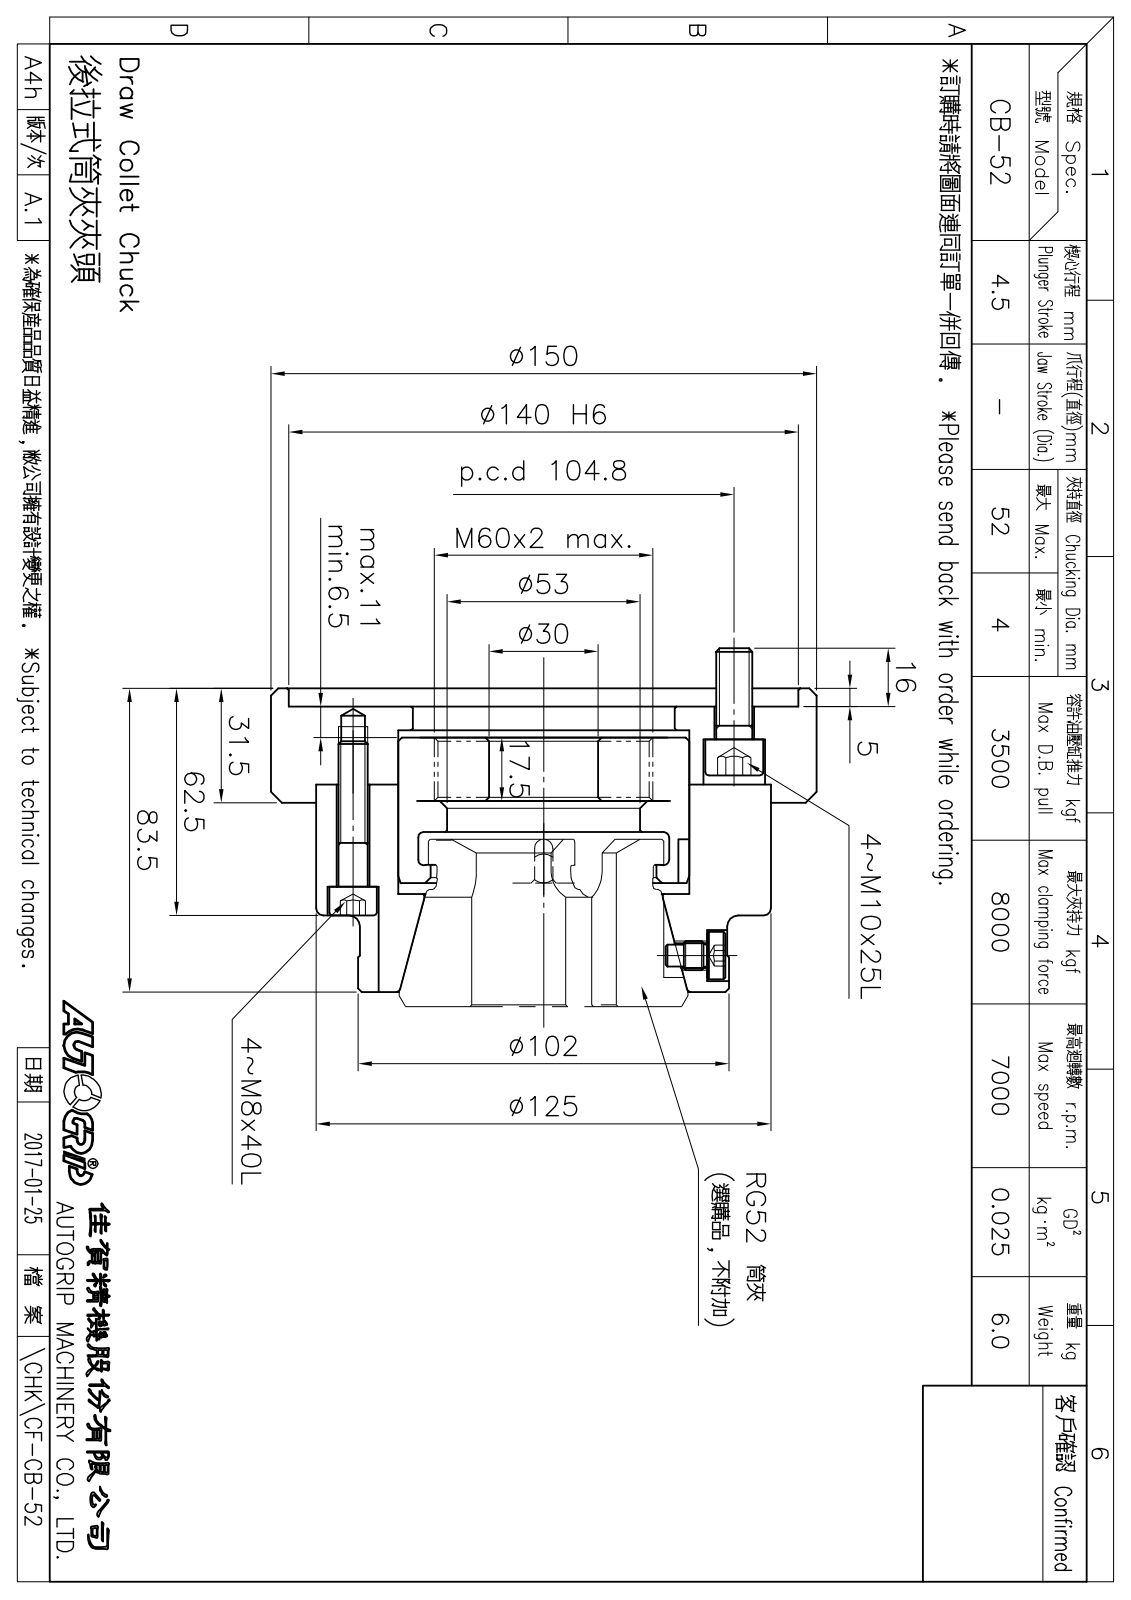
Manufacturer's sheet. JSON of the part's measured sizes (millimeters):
{"part_name": "CF-CB-52-03000; RG52-D40; CF-CB-52-01000; FSW320700 (+4 more)", "step_written_by": "SolidWorks 2020 (CONFIG_CONTROL_DESIGN)", "units": "millimeters", "bodies": {"solids": 13, "faces": 544, "planar": 209, "cylindrical": 167, "other": 168}, "overall_size": [150, 150, 100.95], "volume_mm3": 839910, "surface_area_mm2": 176692, "round_holes": [[5, 8], [6.5, 6], [6.8, 5], [14, 5], [9, 4], [11, 4], [17, 4], [39.8, 1], [53, 1], [58, 1], [62, 1], [65.5, 1]], "round_bosses_or_shafts": [[13, 5], [8, 5], [16, 4], [10, 4], [150, 1], [102, 1], [79.5, 1], [6.8, 1]], "partial_cylinders_radius": [[3, 3], [8, 3], [30, 1], [30.3, 1], [33, 1]], "face_to_face_distances": [21.5, 5, 26.5, 10.5, 15.5, 51, 21, 11, 24.5, 6.5], "hole_center_spacings": [37.89, 40.1, 52.4, 69.07, 74.1, 90.03, 96.82, 58]}
